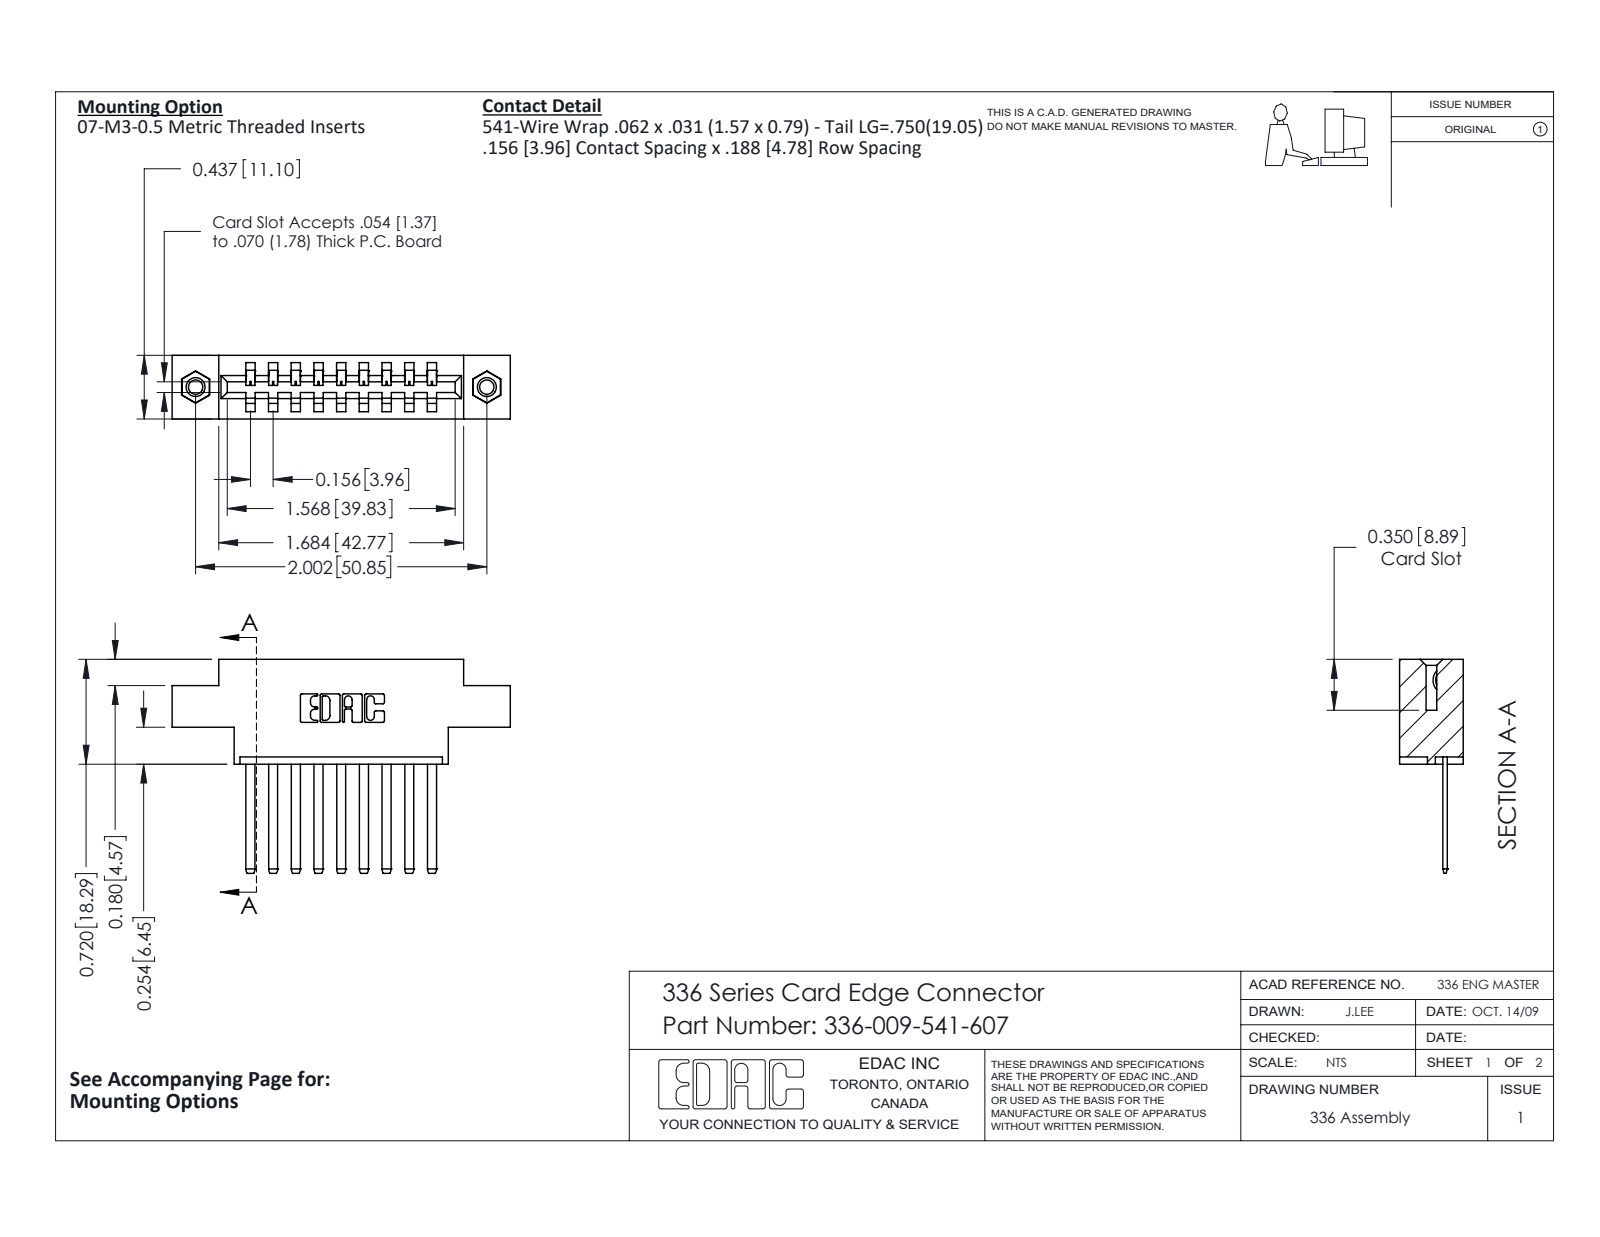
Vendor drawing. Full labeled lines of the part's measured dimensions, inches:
Part name (STEP PRODUCT): 336-290-001_336-290-541; 336-009-541-607; 345-250-001_345-250-005-103; 336 Part_Offset - .156 Dia - TI
STEP written by: SolidWorks 2020 (CONFIG_CONTROL_DESIGN)
Units: inches
Bodies: 12 solids, 628 faces (412 planar, 200 cylindrical, 16 other)
Overall size (bounding box): 2.325 × 1.47 × 0.437
Volume: 0.466 in³ · Surface area: 12.42 in²
Round holes (diameter × count): ⌀0.098 ×2, ⌀0.125 ×2, ⌀0.156 ×2
Round bosses / shafts (diameter × count): ⌀0.155 ×2
Partial cylindrical surfaces — rounded edges, fillets, slot ends (radius × count): R0.01 ×22, R0.004 ×18, R0.056 ×18, R0.007 ×6, R0.031 ×6, R0.026 ×3, R0.022 ×2, R0.04 ×2
Main face-to-face distances: 0.156, 0.437, 0.624, 0.312, 0.468, 0.78, 0.22, 0.376, 0.312, 0.404
Hole centre spacings: 2.002
